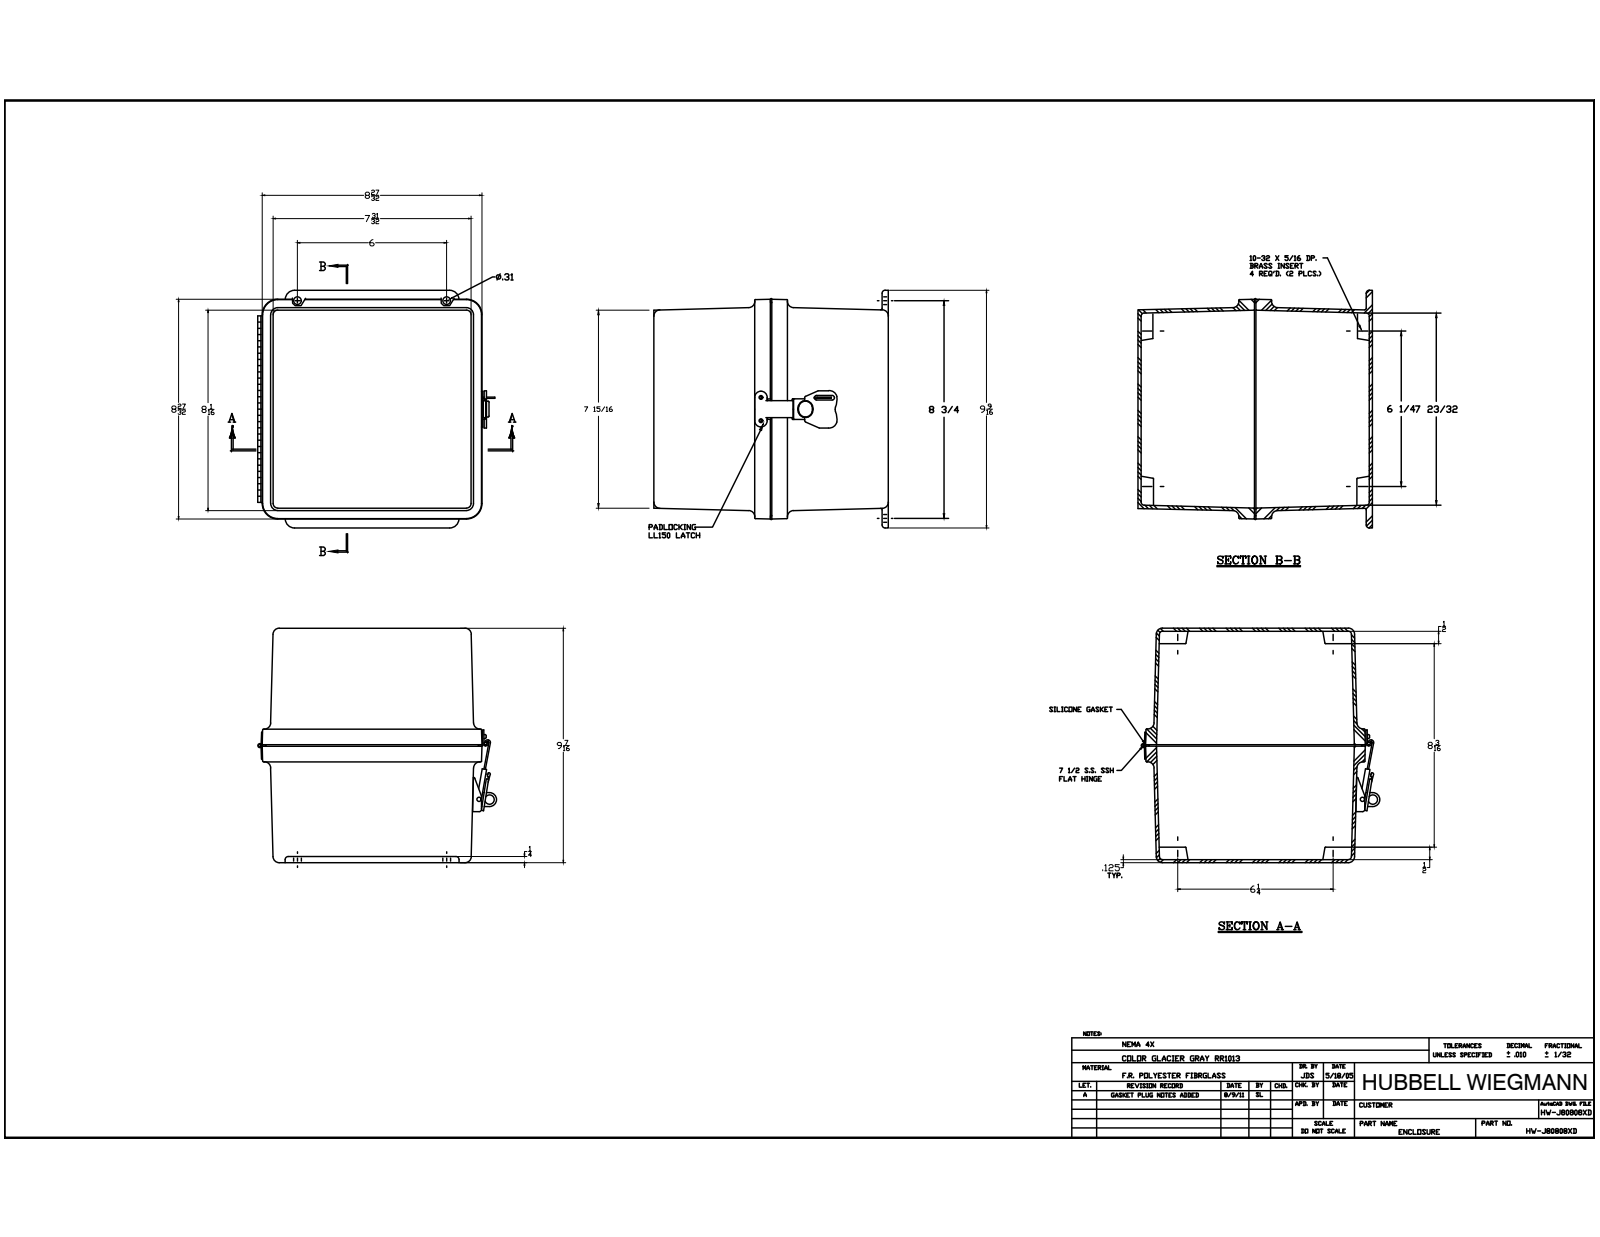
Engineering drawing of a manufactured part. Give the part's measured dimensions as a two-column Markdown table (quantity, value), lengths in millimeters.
| quantity | value |
| --- | --- |
| part name | J808HL_2; RMINS45821P_97; RMINS45821P_98; RMINS45821P_99 (+8 more) |
| STEP written by | Autodesk Inventor 2014 (AUTOMOTIVE_DESIGN) |
| units | millimeters |
| bodies | 35 solids, 1139 faces (401 planar, 443 cylindrical, 295 other) |
| overall size | 242.86 × 242.76 × 239.46 |
| volume | 1 172 000 mm³ |
| surface area | 619 069 mm² |
| round holes (diameter × count) | 3.56 × 10, 3.86 × 10, 3.96 × 7, 3.45 × 6, 5.54 × 4, 3.3 × 2, 4.2 × 2, 5 × 2, 2.16 × 1, 2.7 × 1, 3 × 1, 3.5 × 1 |
| round bosses / shafts (diameter × count) | 6.35 × 10, 3.17 × 10, 6.86 × 7, 14.8 × 1, 13.3 × 1, 5.3 × 1, 4.7 × 1, 3.94 × 1 |
| partial cylindrical surfaces (radius × count) | 0.79 × 88, 6.35 × 20, 3.17 × 12, 2 × 10, 0.79 × 8, 19.05 × 5, 0.95 × 4, 1 × 4 |
| main face-to-face distances | 3.17, 3.18, 205.37, 202.21, 202.2, 233.11, 239.46, 236.29, 236.28, 205.39 |
| hole center spacings | 184.12, 158.75, 158.76, 258.19, 33.67, 76.2, 88.9, 165.1 |
